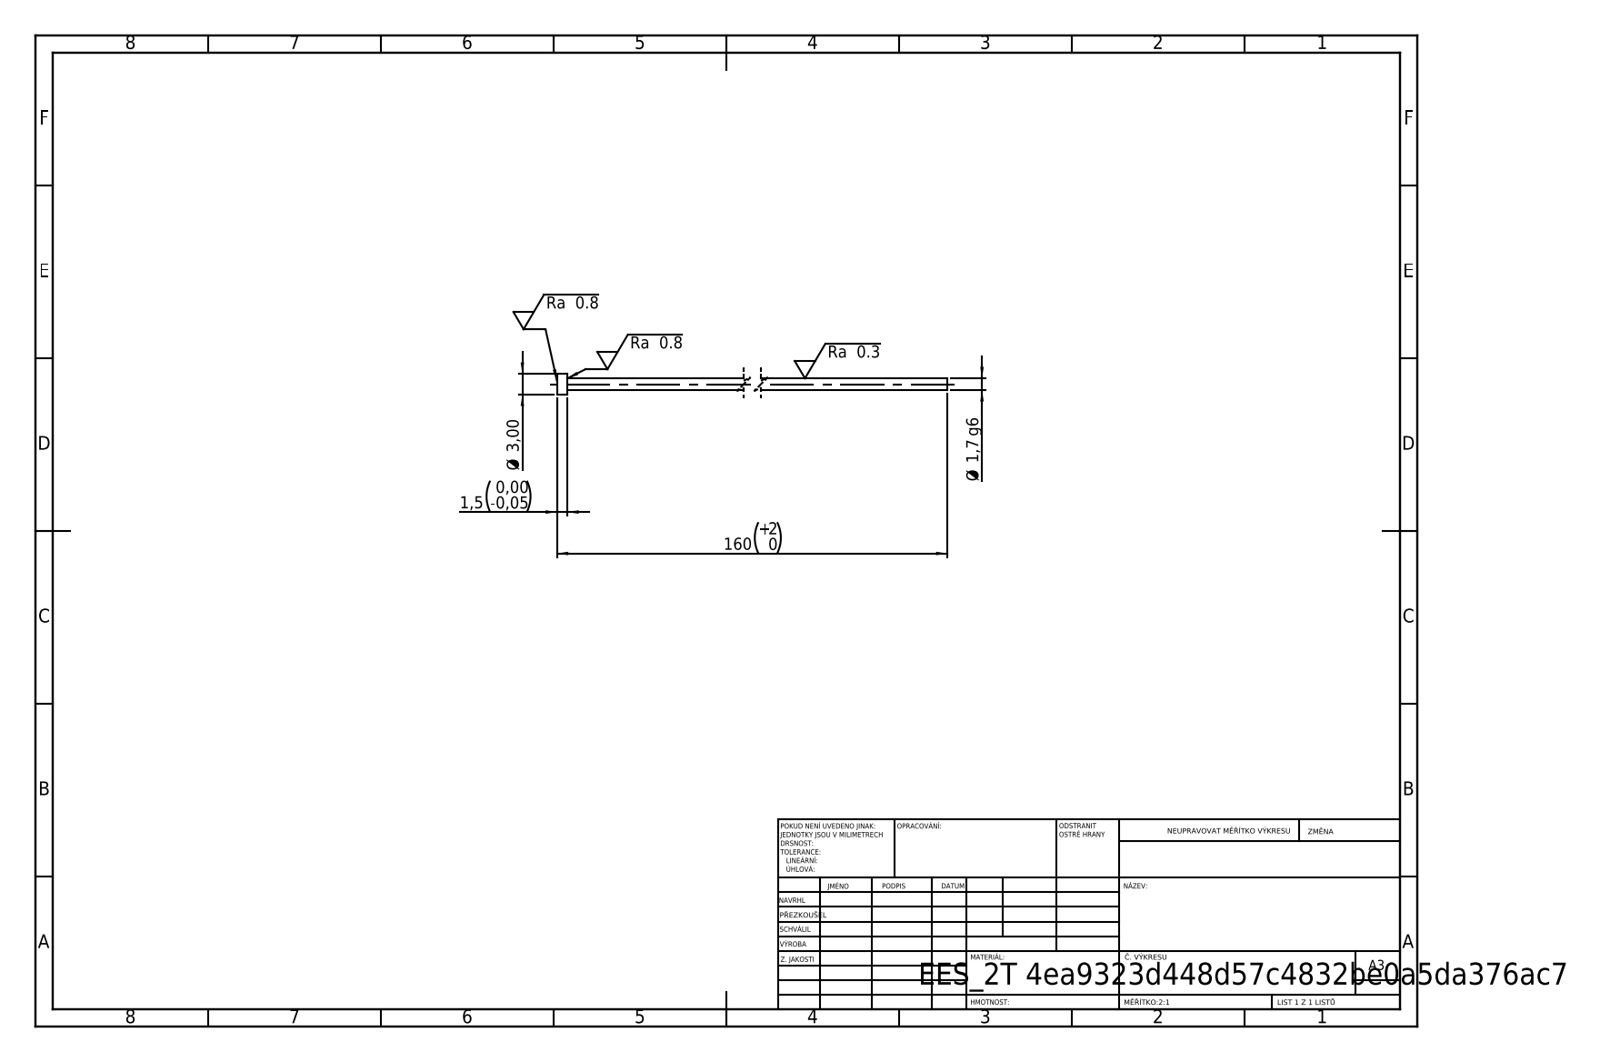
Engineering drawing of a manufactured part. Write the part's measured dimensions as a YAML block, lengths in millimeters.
step_written_by: "SolidWorks 2019 (CONFIG_CONTROL_DESIGN)"
units: millimeters
bodies: {solids: 1, faces: 7, planar: 3, cylindrical: 4, other: 0}
overall_size: [160, 3, 3]
volume: 370
surface_area: 875
round_bosses_or_shafts:
  - {diameter: 3, count: 1}
  - {diameter: 1.7, count: 1}
face_to_face_distances: [1.5, 160, 158.5]
